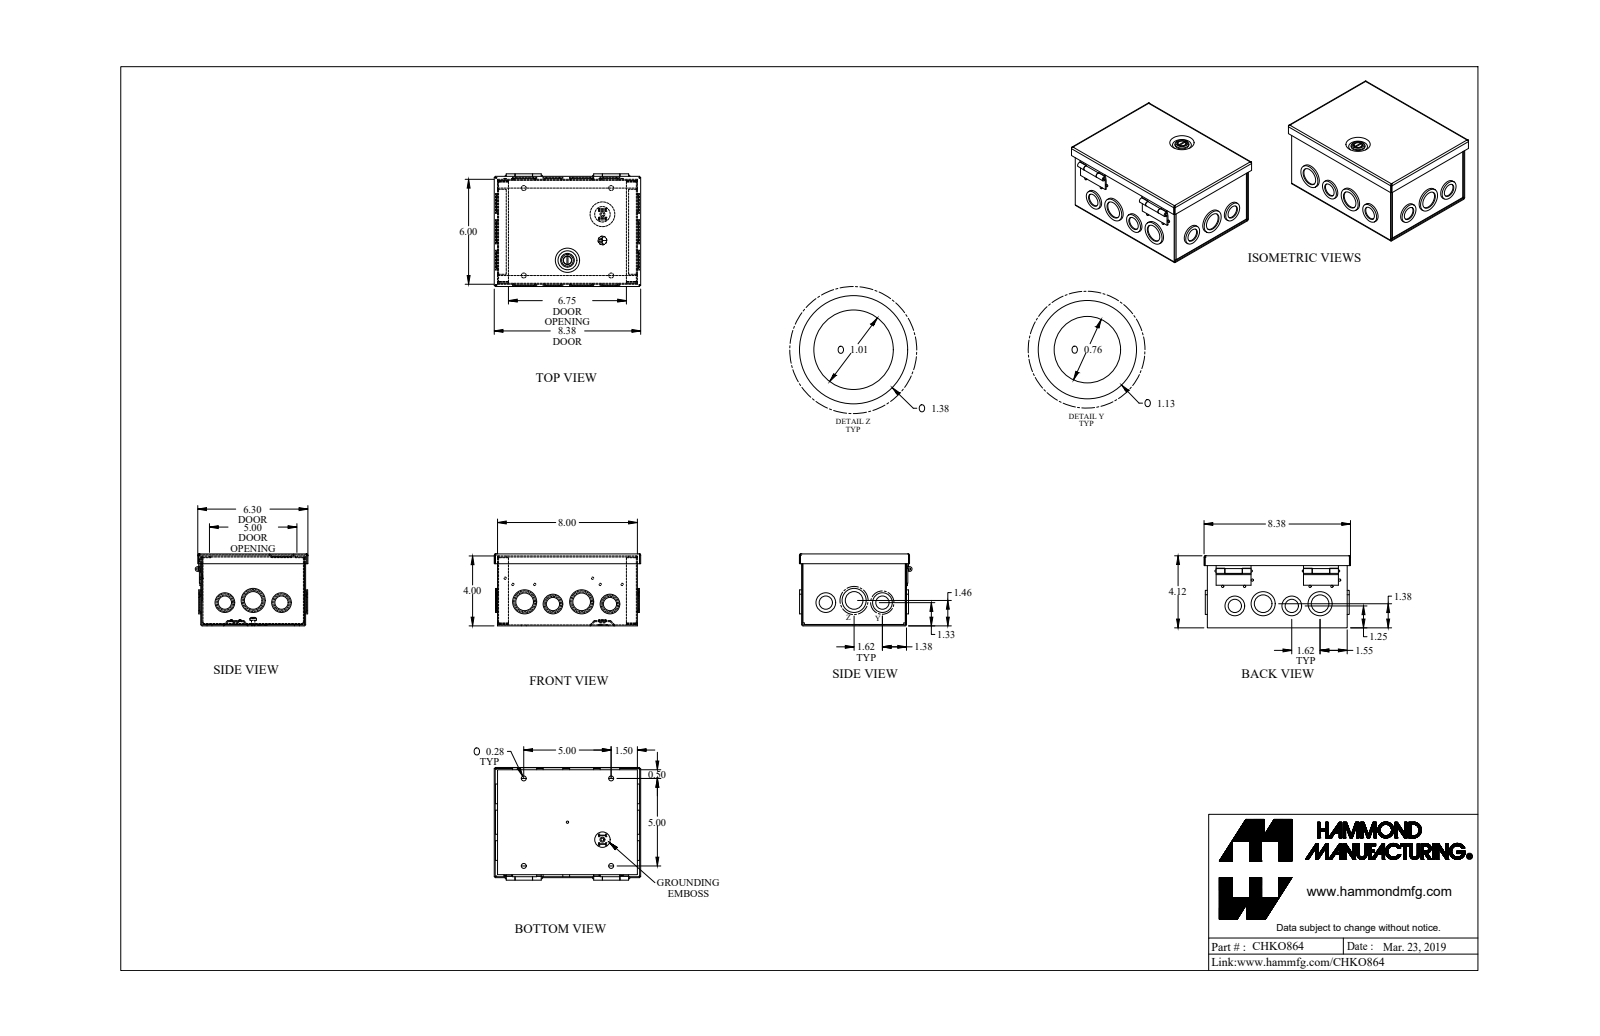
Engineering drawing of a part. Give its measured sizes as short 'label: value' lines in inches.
name: CHKO864_Default
written by: SolidWorks 2019 (CONFIG_CONTROL_DESIGN)
unit: in
bodies: 12 solids, 655 faces (328 planar, 284 cylindrical, 43 other)
size: 8.38 × 6.443 × 4.118
volume: 15.61 in³; area: 549 in²
holes: 7× ⌀1.011, 4× ⌀0.281, 4× ⌀0.761, 3× ⌀1.261, 1× ⌀0.125, 1× ⌀0.17, 1× ⌀0.319, 1× ⌀0.476, 1× ⌀0.5
bosses: 8× ⌀0.131, 6× ⌀1.125, 4× ⌀0.875, 3× ⌀1.375, 2× ⌀0.875, 1× ⌀1.125, 1× ⌀0.787, 1× ⌀0.547
rounds: 16× R0.029, 16× R0.086, 8× R0.057, 4× R0.012, 4× R0.1, 2× R0.036, 2× R0.079, 2× R0.25
face distances: 0.057, 4.061, 5.943, 4.118, 4.004, 7.943, 6, 5.886, 8, 3.943
hole spacings: 1.625, 5, 3.26, 7.071, 1.5, 1.581, 1.644, 2.061
